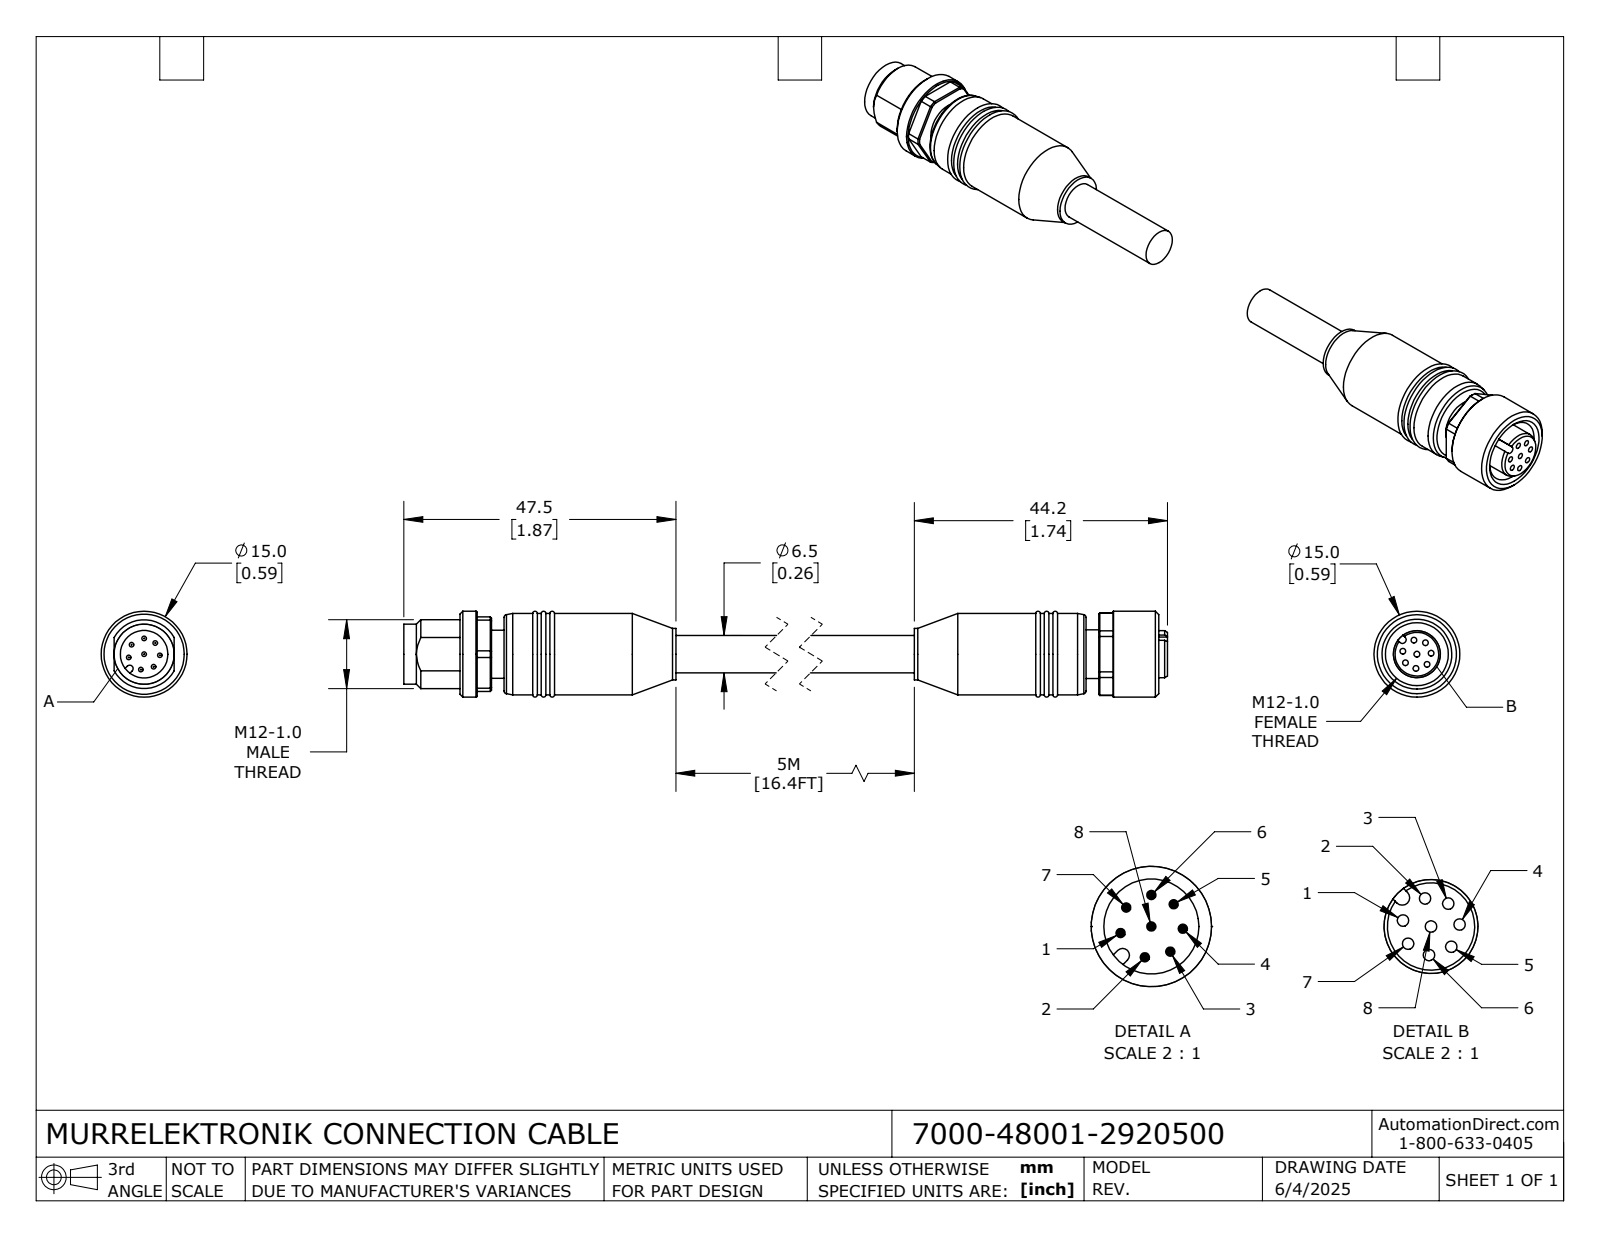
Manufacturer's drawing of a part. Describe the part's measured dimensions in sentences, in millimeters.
The part is named "7000-48001-2920500_FEMALE; 7000-48001-2920500; 7000-48001-2920500_MALE". Its 3-D file was written by "SolidWorks 2024 (CONFIG_CONTROL_DESIGN)". It is 2 solids with 222 faces: 64 planar, 89 cylindrical and 69 other. Overall it measures 156.7 by 15 by 15 millimeters. Its volume is 13 206 cubic millimeters and its surface area 6 614 square millimeters. Round holes: 8 of diameter 1, 1 of diameter 8.3, 1 of diameter 11. Round bosses or shafts: 8 of diameter 0.8, 1 of diameter 15, 1 of diameter 14.2, 1 of diameter 10.5, 1 of diameter 9, 1 of diameter 8.5, 1 of diameter 8.4, 1 of diameter 8.2. Partial cylindrical surfaces (rounded edges, fillets, slot ends): 1 of radius 0.6, 1 of radius 0.65, 1 of radius 6, 1 of radius 7.2. The main face-to-face distances are 2.2, 127.2, 13, 129.4, 10.5, 125, 134.9, 52.2, 77.2, 50. The hole center spacings are 2.5, 2.07, 3.78, 4.95, 2.08, 4.22, 4.79, 4.8.
